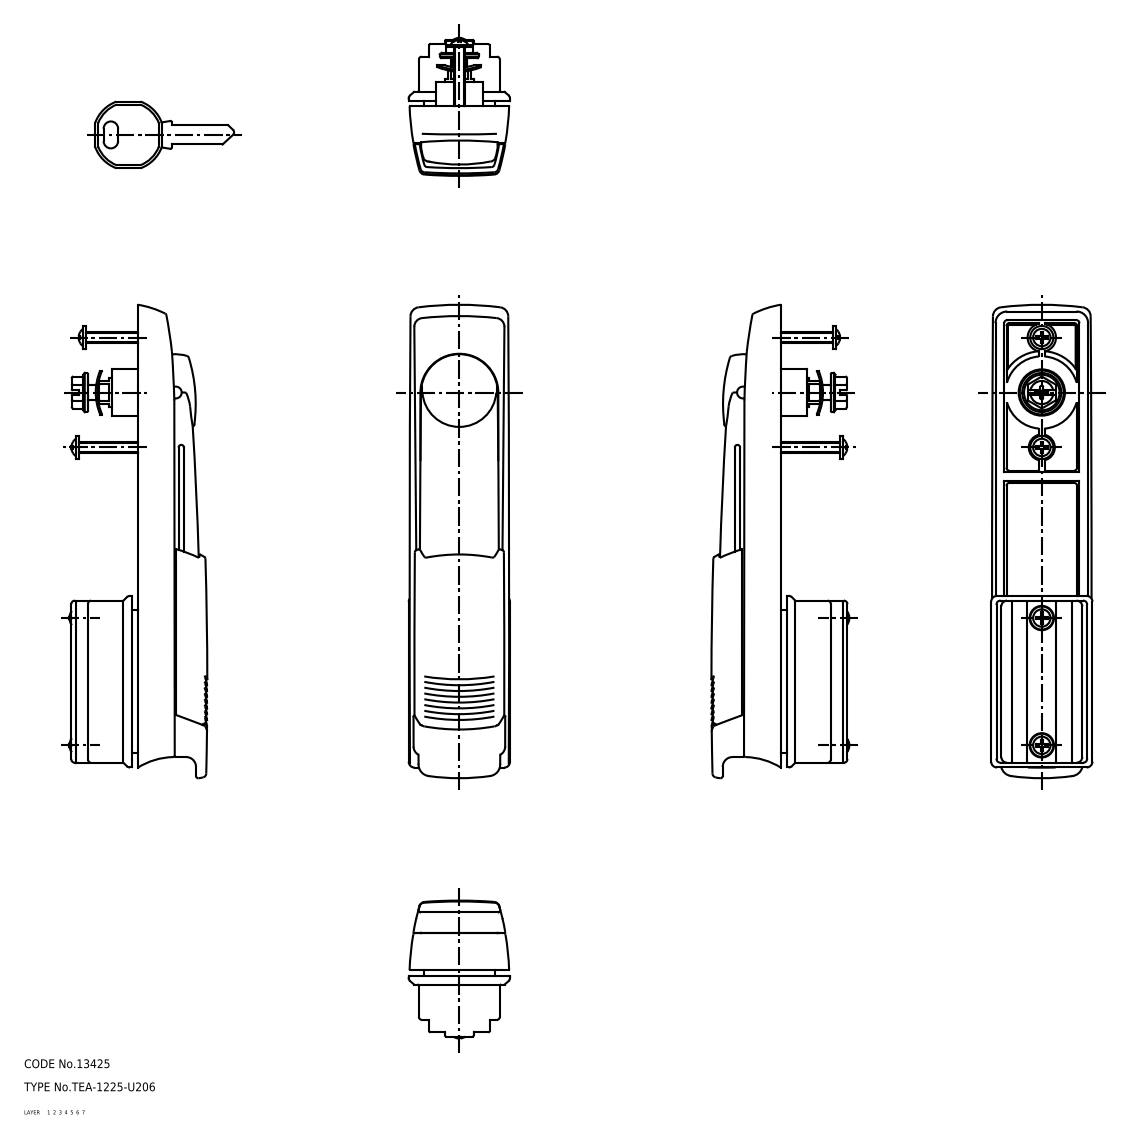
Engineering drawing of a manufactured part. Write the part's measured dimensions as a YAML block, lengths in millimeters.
part_name: "handle; cover; bracket; base (+4 more)"
step_written_by: "CADfix (AUTOMOTIVE_DESIGN)"
units: millimeters
bodies: {solids: 7, faces: 545, planar: 0, cylindrical: 0, other: 545}
overall_size: [163.65, 150.75, 35]
volume: 99687
surface_area: 52582
